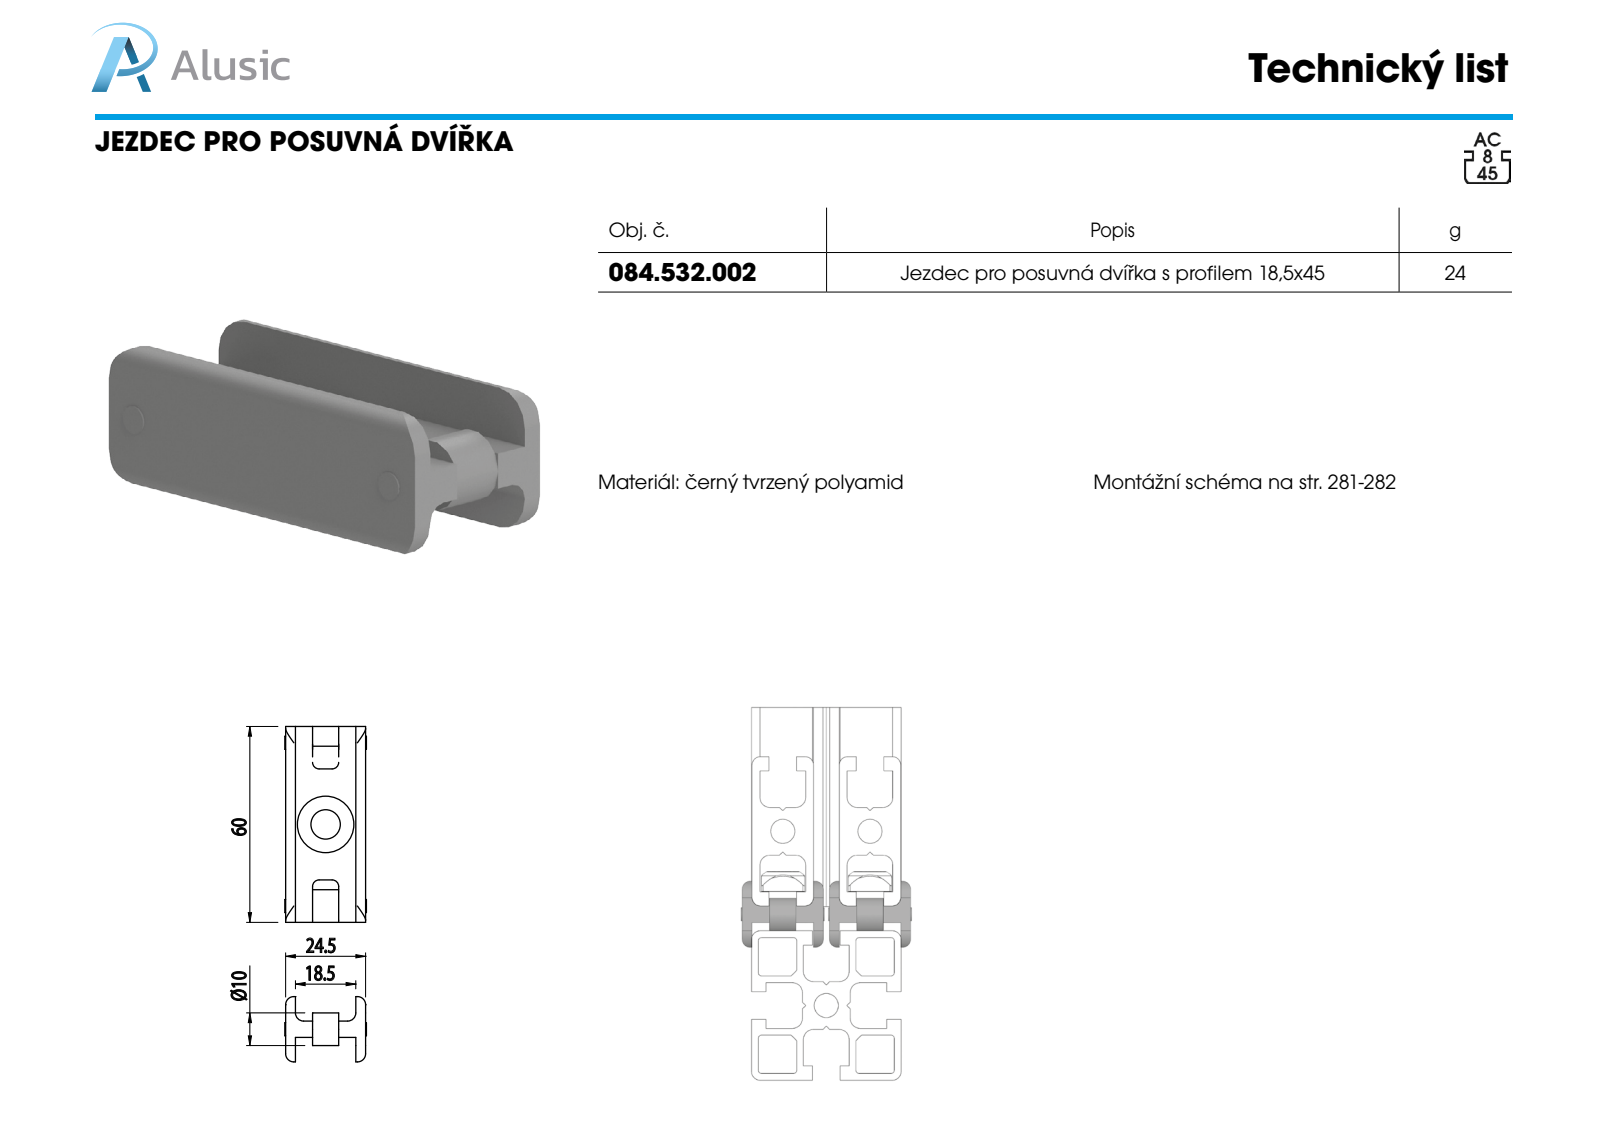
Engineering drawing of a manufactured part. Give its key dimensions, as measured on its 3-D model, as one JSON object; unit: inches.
{"part_name": "084.532.002", "step_written_by": "SolidWorks 2011 (CONFIG_CONTROL_DESIGN)", "units": "inches", "bodies": {"solids": 3, "faces": 72, "planar": 42, "cylindrical": 28, "other": 2}, "overall_size": [2.362, 0.984, 0.787], "volume_in3": 0.804, "surface_area_in2": 12.45, "round_holes": [[0.217, 1]], "round_bosses_or_shafts": [[0.394, 2], [0.157, 2]], "partial_cylinders_radius": [[0.098, 6], [0.079, 4], [0.197, 4]], "face_to_face_distances": [0.118, 0.846, 0.965, 0.728, 0.197, 0.325, 0.64, 0.207, 0.522, 2.362]}
